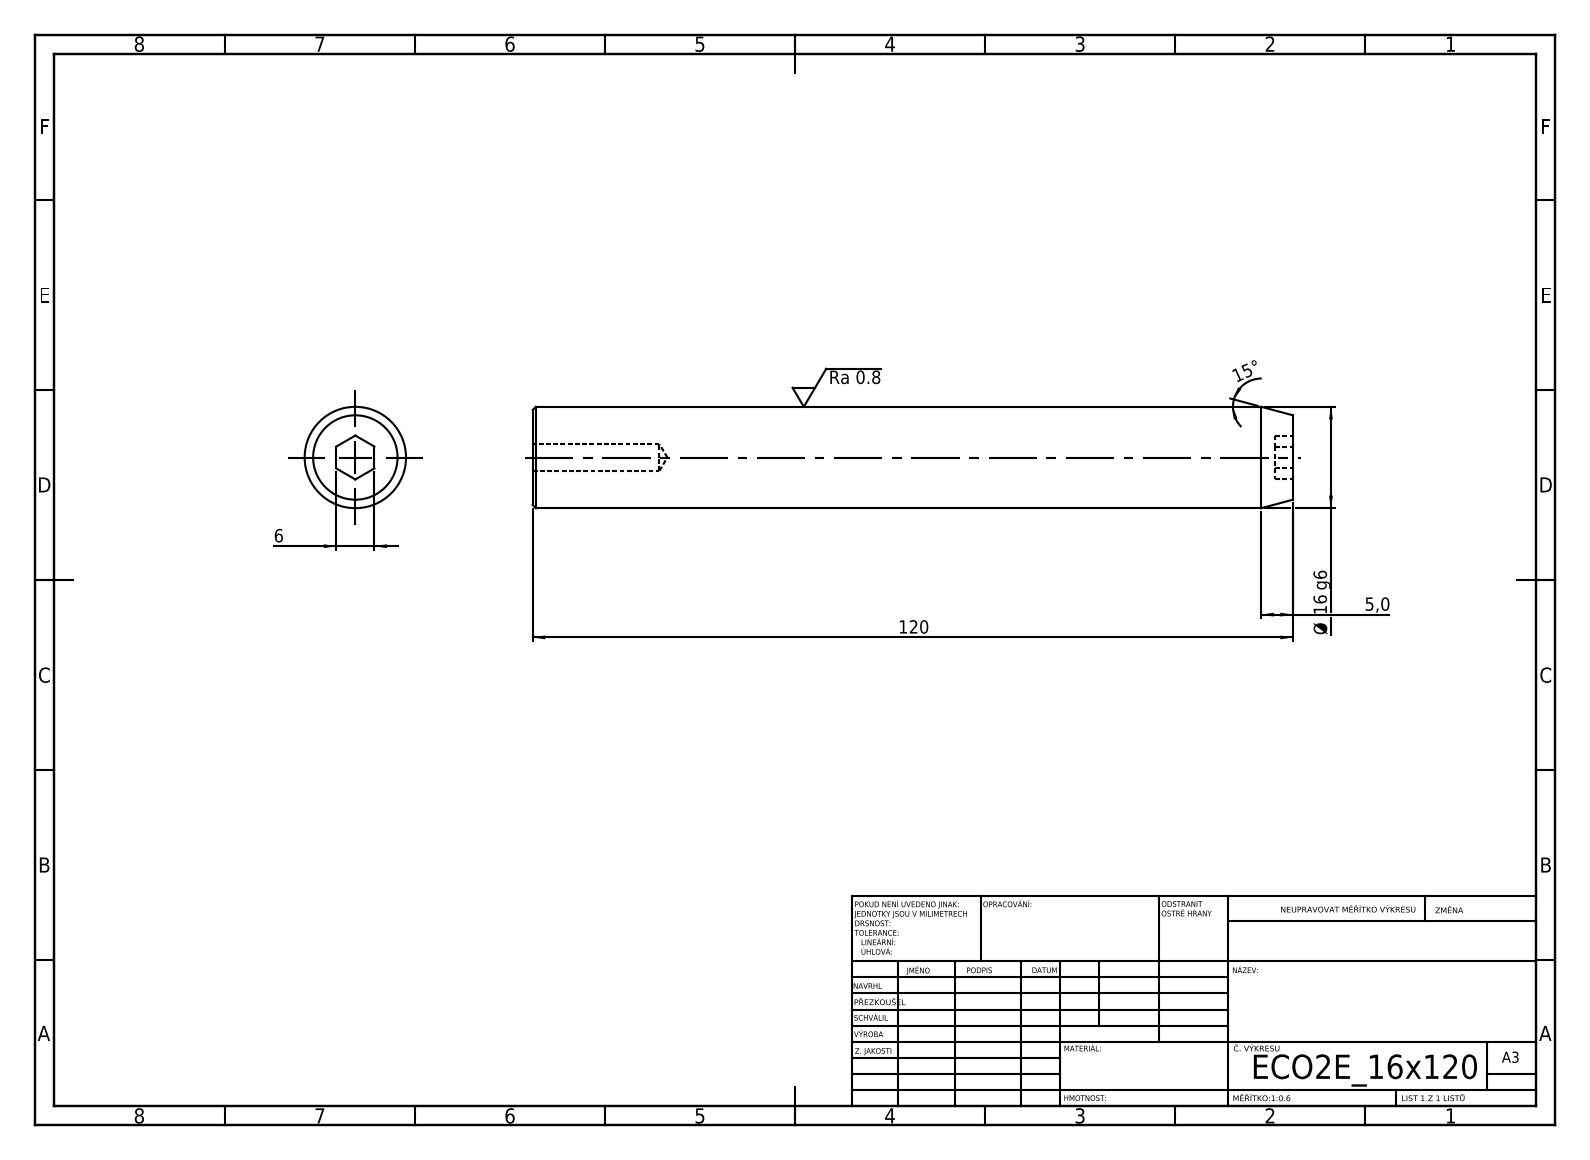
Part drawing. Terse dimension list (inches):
written by: SolidWorks 2019 (CONFIG_CONTROL_DESIGN)
unit: in
bodies: 1 solid, 19 faces (9 planar, 4 cylindrical, 6 other)
size: 4.724 × 0.63 × 0.63
volume: 1.44 in³; area: 10.34 in²
holes: 1× ⌀0.165
bosses: 1× ⌀0.63
face distances: 4.724, 0.11, 4.614, 0.236
